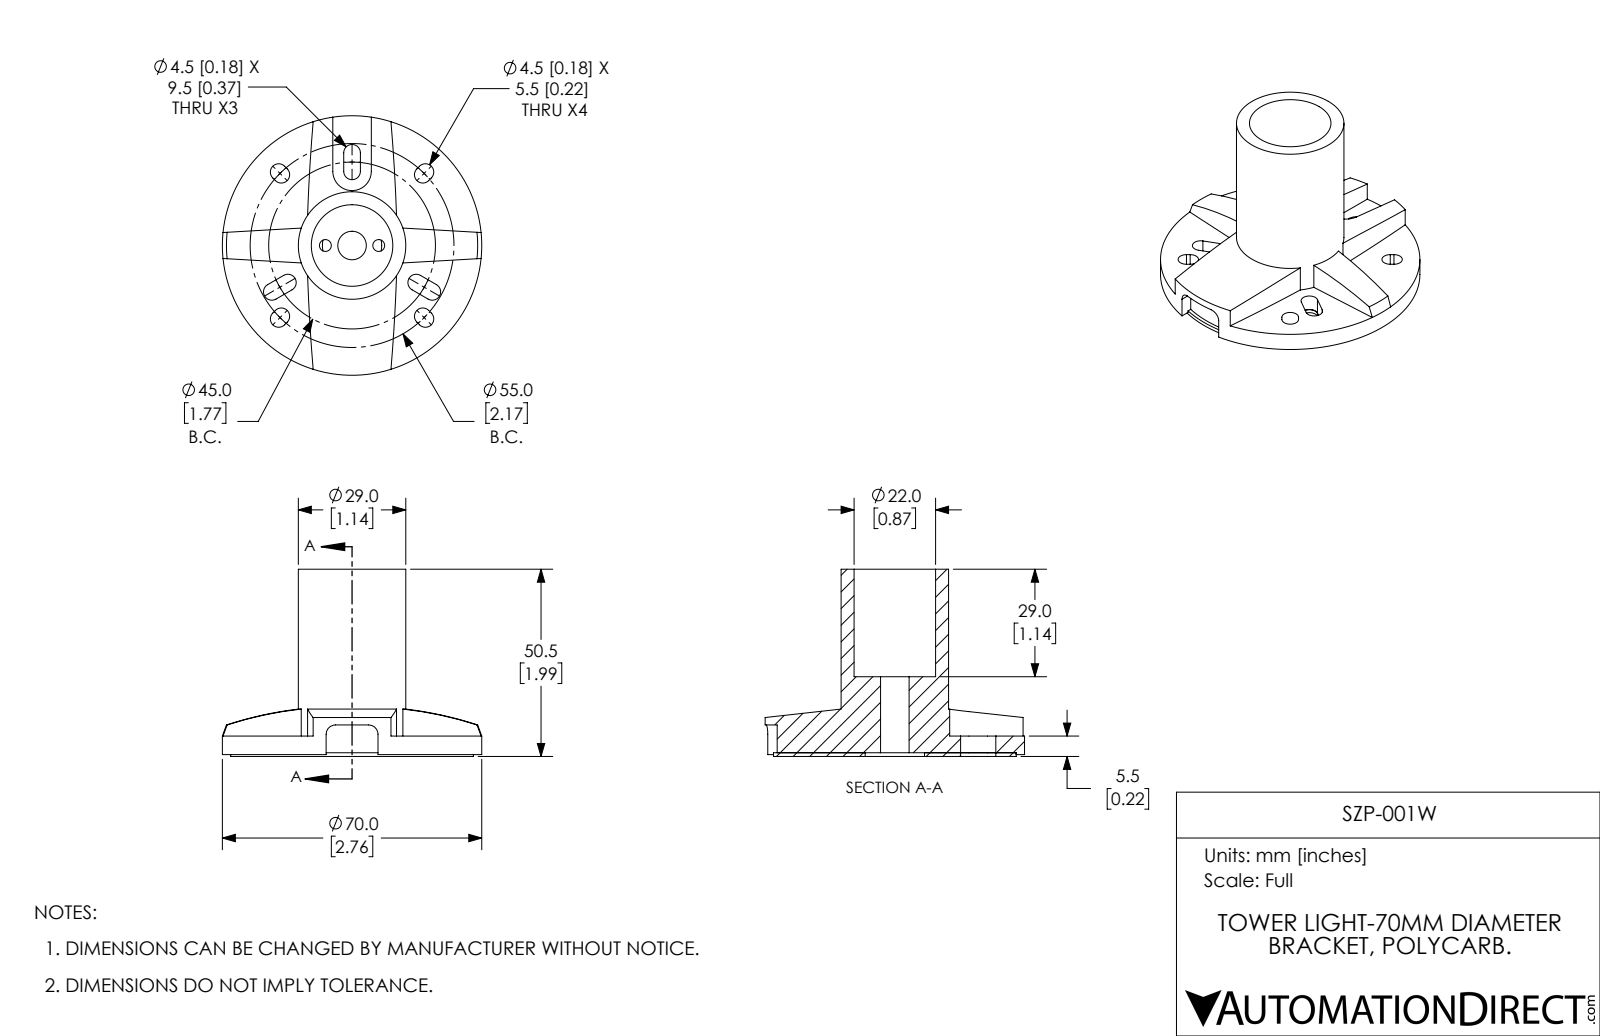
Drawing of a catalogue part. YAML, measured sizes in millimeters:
part_name: "SZP-001W"
step_written_by: "SolidWorks 2017 (AUTOMOTIVE_DESIGN)"
units: millimeters
bodies: {solids: 2, faces: 121, planar: 44, cylindrical: 69, other: 8}
overall_size: [70, 70, 50.5]
volume: 43390
surface_area: 23390
round_holes:
  - {diameter: 3.2, count: 2}
  - {diameter: 7.7, count: 1}
  - {diameter: 16, count: 1}
  - {diameter: 22, count: 1}
round_bosses_or_shafts:
  - {diameter: 70, count: 1}
  - {diameter: 65.5, count: 1}
  - {diameter: 29, count: 1}
partial_cylinders:
  - {radius: 2.3, count: 14}
  - {radius: 505.4, count: 4}
  - {radius: 2.5, count: 2}
  - {radius: 5.2, count: 1}
  - {radius: 31.8, count: 1}
face_to_face_distances: [1, 4.5, 5.5, 0.5, 5, 21.5, 21, 20.5, 16, 50.5]
hole_center_spacings: [7.2, 14.4]
